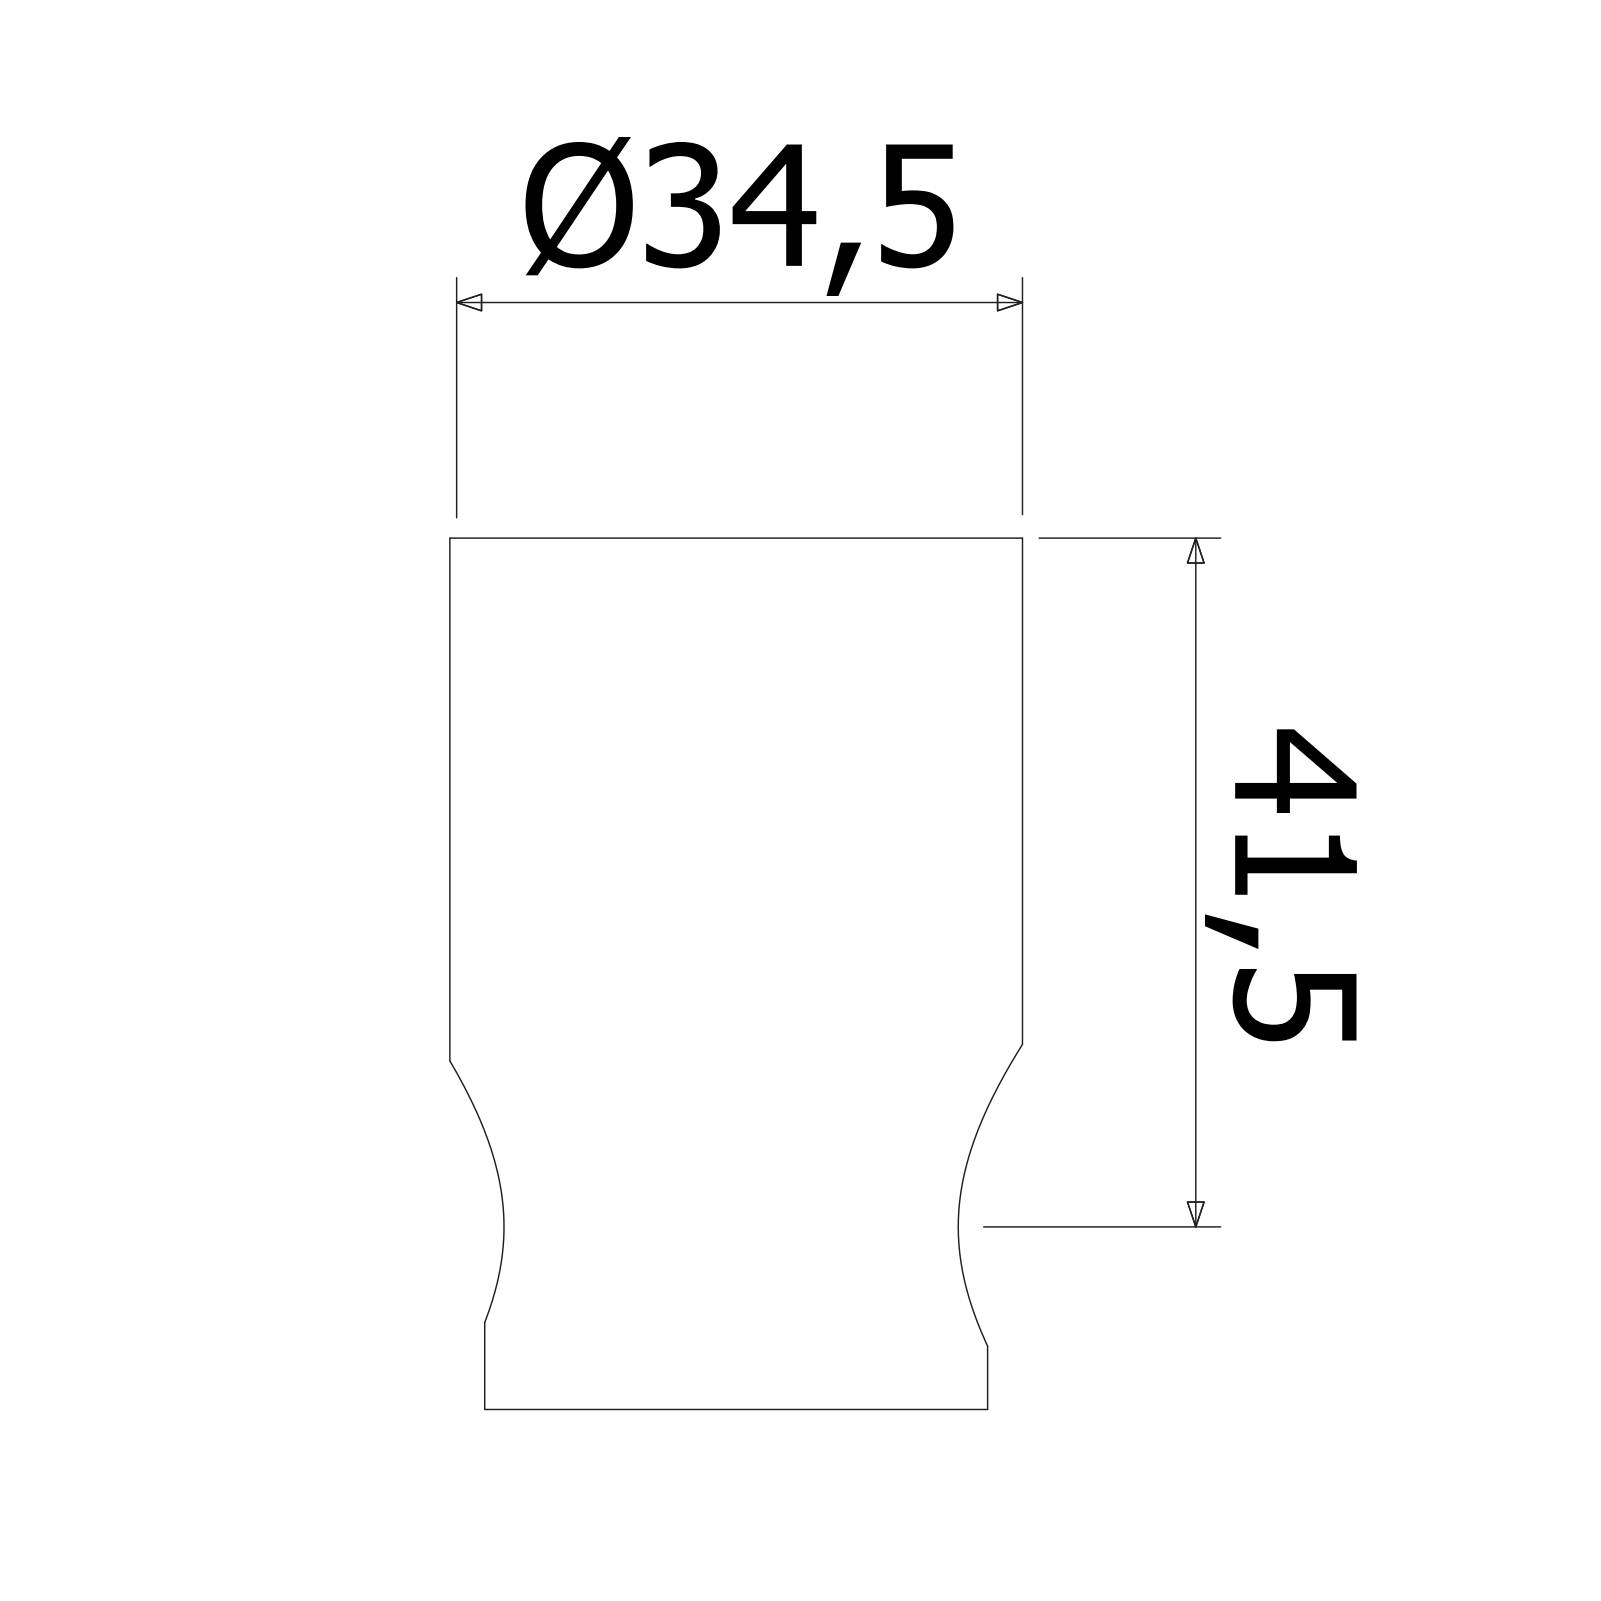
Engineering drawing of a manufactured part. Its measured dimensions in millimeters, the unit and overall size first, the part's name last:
Units: millimetres
Overall size (bounding box): 52.5 × 34.5 × 34.5
Round holes (diameter × count): ⌀9 ×2, ⌀29.5 ×1
Round bosses / shafts (diameter × count): ⌀11 ×2, ⌀34.5 ×1
Partial cylindrical surfaces — rounded edges, fillets, slot ends (radius × count): R2.5 ×4, R13.5 ×1
Main face-to-face distances: 52.5, 5.25, 21.75, 16.5, 27, 8.5, 44, 11, 16, 5.75
Hole centre spacings: 8.25, 16.5
Volume: 17 623 mm³ · Surface area: 15 248 mm²
Bodies: 1 solid, 35 faces (17 planar, 17 cylindrical, 1 other)
Part name (STEP PRODUCT): ZSUP010CR
STEP written by: CREO PARAMETRIC BY PTC INC, 2020044 (CONFIG_CONTROL_DESIGN)
